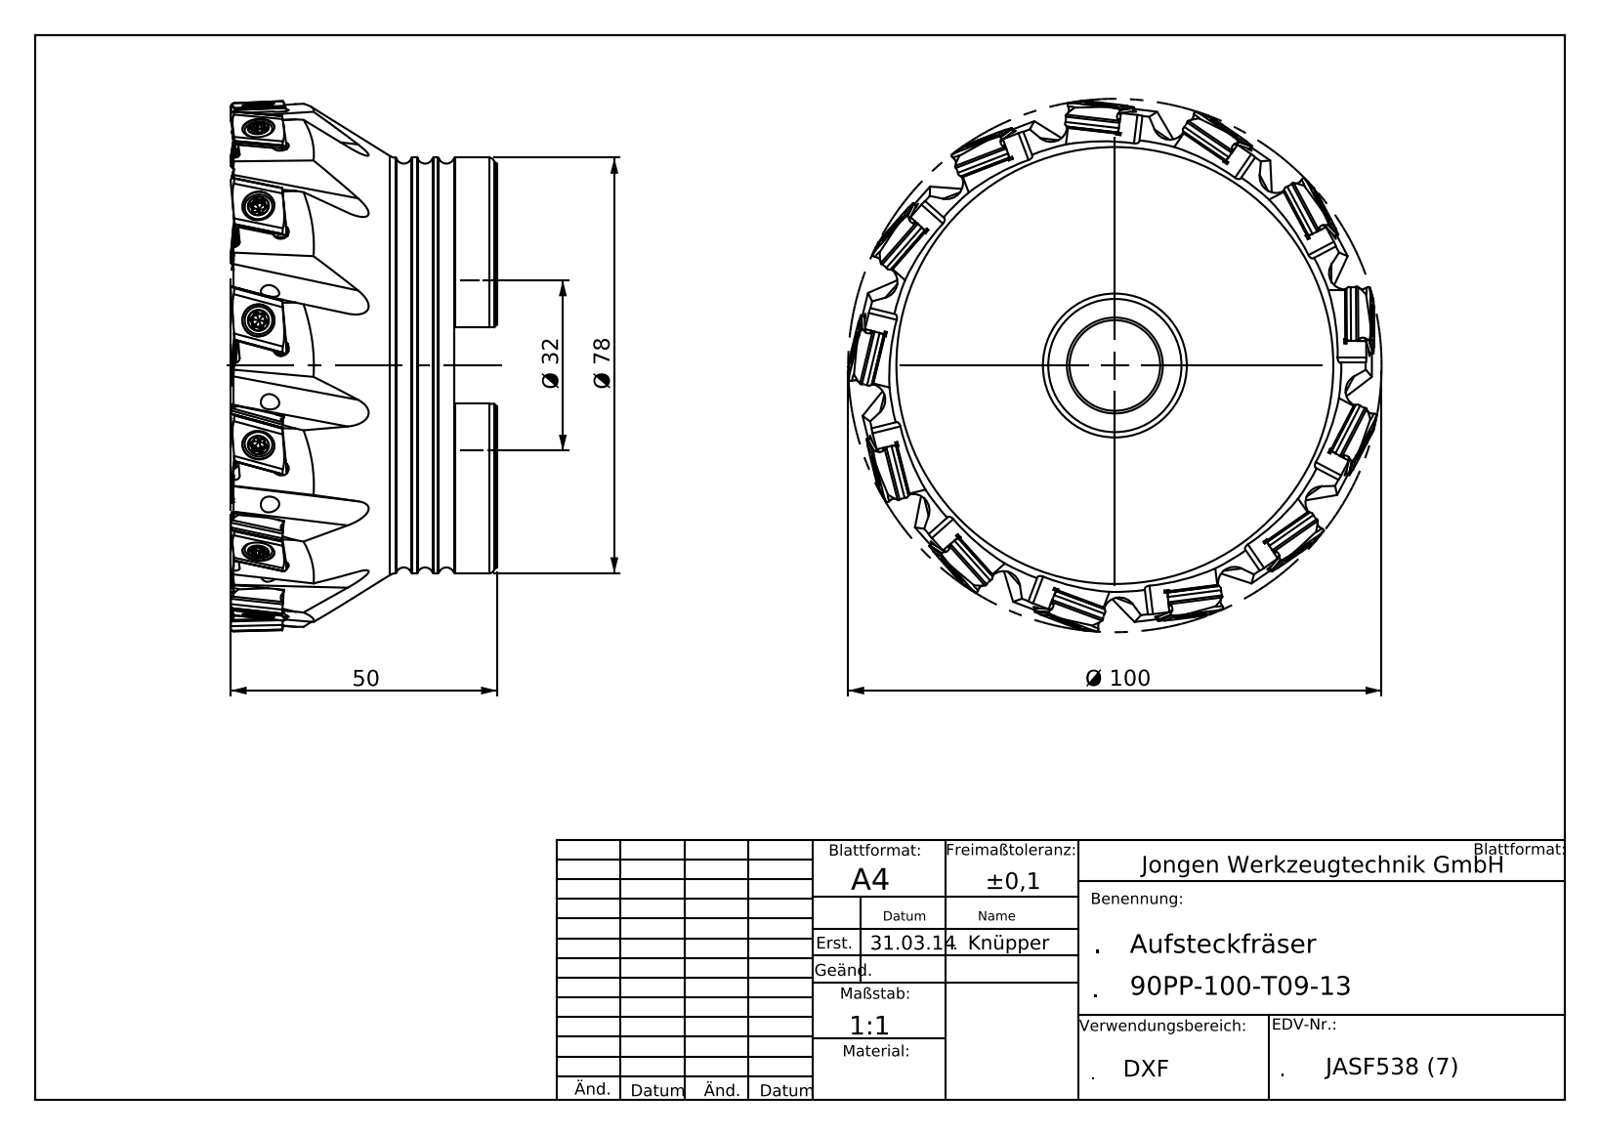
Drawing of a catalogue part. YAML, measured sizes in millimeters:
part_name: "90PP_100_T09_12"
step_written_by: "SolidWorks 2015 (AUTOMOTIVE_DESIGN)"
units: millimeters
bodies: {solids: 1, faces: 326, planar: 132, cylindrical: 88, other: 106}
overall_size: [99.98, 99.98, 50.1]
volume: 238048
surface_area: 40607
round_holes:
  - {diameter: 3, count: 13}
  - {diameter: 3.3, count: 13}
  - {diameter: 17, count: 1}
  - {diameter: 25, count: 1}
  - {diameter: 32, count: 1}
  - {diameter: 32.15, count: 1}
  - {diameter: 32.3, count: 1}
round_bosses_or_shafts:
  - {diameter: 99.98, count: 1}
  - {diameter: 78, count: 1}
partial_cylinders:
  - {radius: 0.9, count: 13}
  - {radius: 1.5, count: 13}
  - {radius: 3, count: 13}
face_to_face_distances: [46.9, 8, 38.9, 25, 17, 21.9, 14.4, 30.9, 22.9, 5.9]
